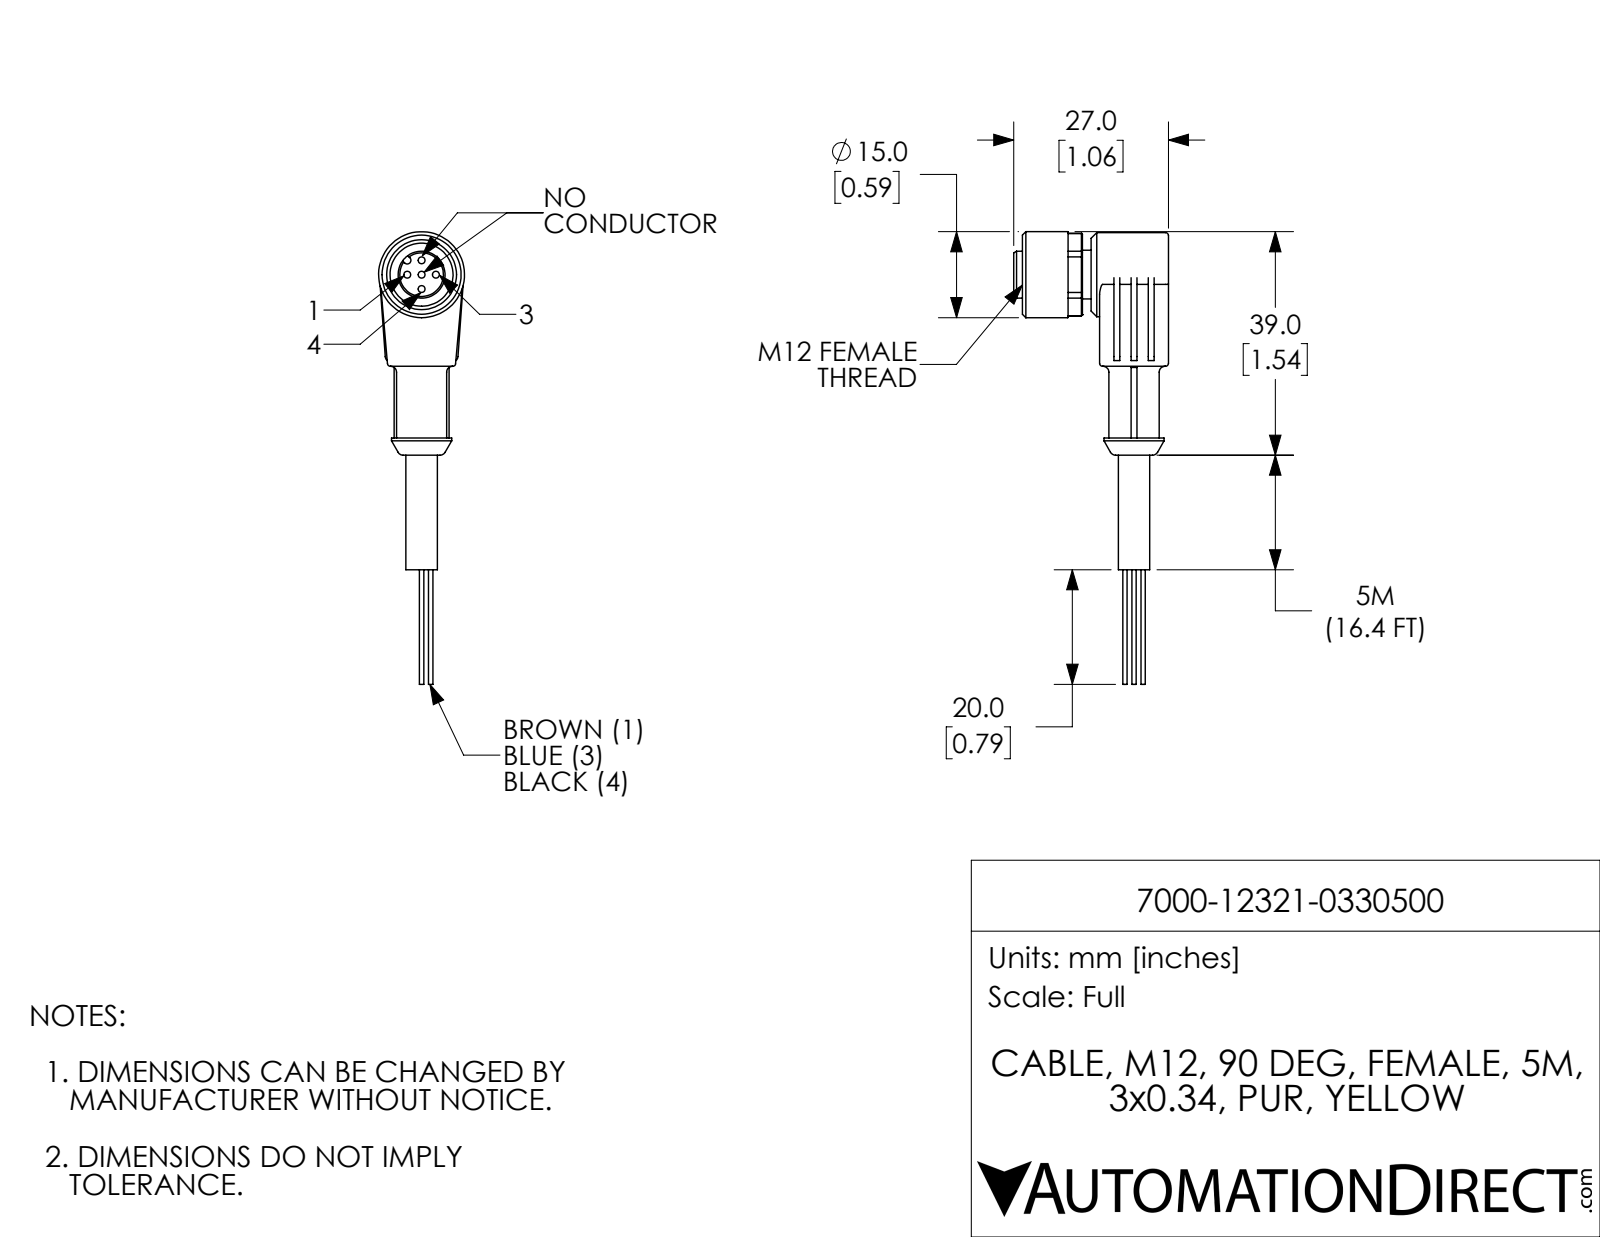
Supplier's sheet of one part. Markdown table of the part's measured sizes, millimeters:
| quantity | value |
| --- | --- |
| part name | 7000-12321-0330500 |
| STEP written by | SolidWorks 2021 (CONFIG_CONTROL_DESIGN) |
| units | millimeters |
| bodies | 1 solid, 149 faces (64 planar, 57 cylindrical, 28 other) |
| overall size | 79 × 27 × 15 |
| volume | 6 830 mm³ |
| surface area | 3 756 mm² |
| round holes (diameter × count) | 1.2 × 5, 4.8 × 1, 11 × 1 |
| round bosses / shafts (diameter × count) | 0.8 × 3, 15 × 1, 14.7 × 1, 10.5 × 1, 8.8 × 1, 8.5 × 1, 8.2 × 1, 5.5 × 1 |
| partial cylindrical surfaces (radius × count) | 0.5 × 8, 1 × 2, 0.7 × 1, 7.2 × 1 |
| main face-to-face distances | 12, 1.5, 3, 13.5, 15, 5.5, 9.5, 6, 8, 12.5 |
| hole center spacings | 2.5, 3.5, 5 |
